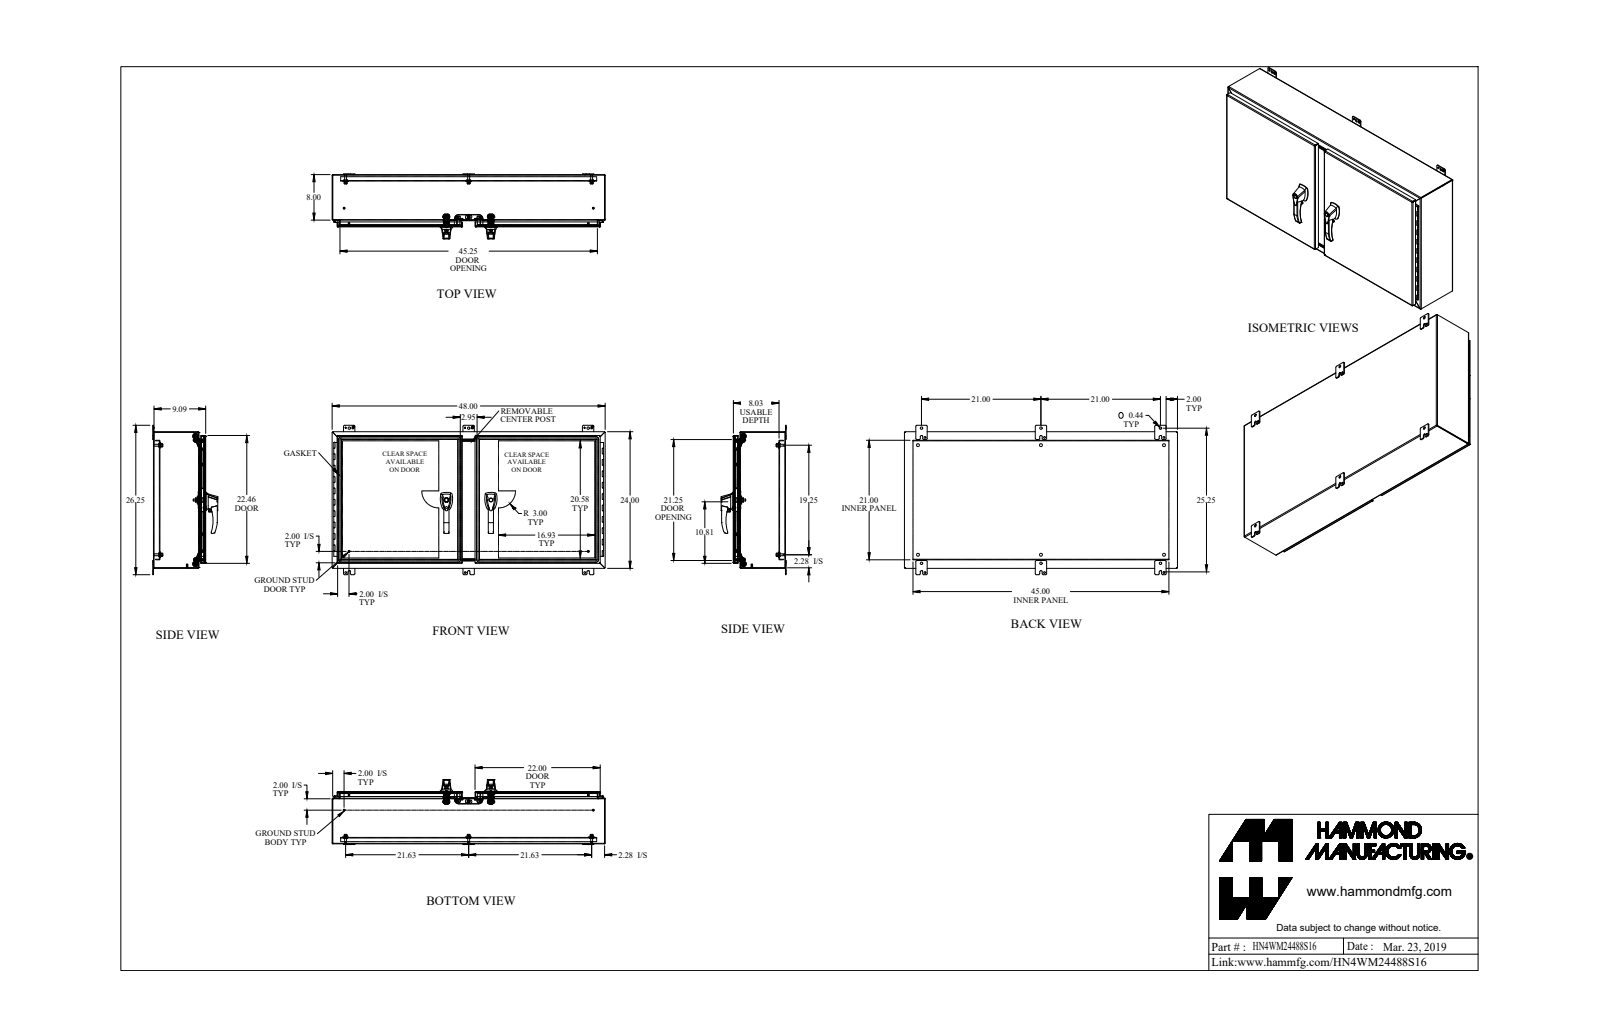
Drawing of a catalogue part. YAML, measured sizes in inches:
part_name: "HN4WM24488S16"
step_written_by: "SolidWorks 2018 (AUTOMOTIVE_DESIGN)"
units: inches
bodies: {solids: 106, faces: 2648, planar: 1251, cylindrical: 1117, other: 280}
overall_size: [48, 26.25, 11.425]
volume: 529.7
surface_area: 10960
round_holes:
  - {diameter: 0.25, count: 10}
  - {diameter: 0.313, count: 9}
  - {diameter: 0.304, count: 8}
  - {diameter: 0.201, count: 6}
  - {diameter: 0.307, count: 6}
  - {diameter: 0.5, count: 6}
  - {diameter: 0.257, count: 4}
  - {diameter: 0.28, count: 4}
  - {diameter: 0.281, count: 4}
  - {diameter: 0.313, count: 4}
  - {diameter: 0.39, count: 4}
  - {diameter: 0.413, count: 4}
round_bosses_or_shafts:
  - {diameter: 1, count: 10}
  - {diameter: 0.65, count: 6}
  - {diameter: 0.375, count: 6}
  - {diameter: 0.332, count: 6}
  - {diameter: 0.293, count: 6}
  - {diameter: 0.75, count: 4}
  - {diameter: 0.63, count: 4}
  - {diameter: 0.625, count: 4}
partial_cylinders:
  - {radius: 0.125, count: 37}
  - {radius: 0.018, count: 32}
  - {radius: 0.188, count: 27}
  - {radius: 0.25, count: 26}
  - {radius: 0.06, count: 22}
  - {radius: 0.5, count: 22}
  - {radius: 0.048, count: 19}
  - {radius: 0.143, count: 19}
face_to_face_distances: [0.095, 1.032, 0.095, 9.09, 8.995, 9.185, 9.09, 1.127, 7.963, 8.058]
hole_center_spacings: [21.625, 6, 7.814, 19.651, 20.163, 26.909, 27.286, 28.952]
